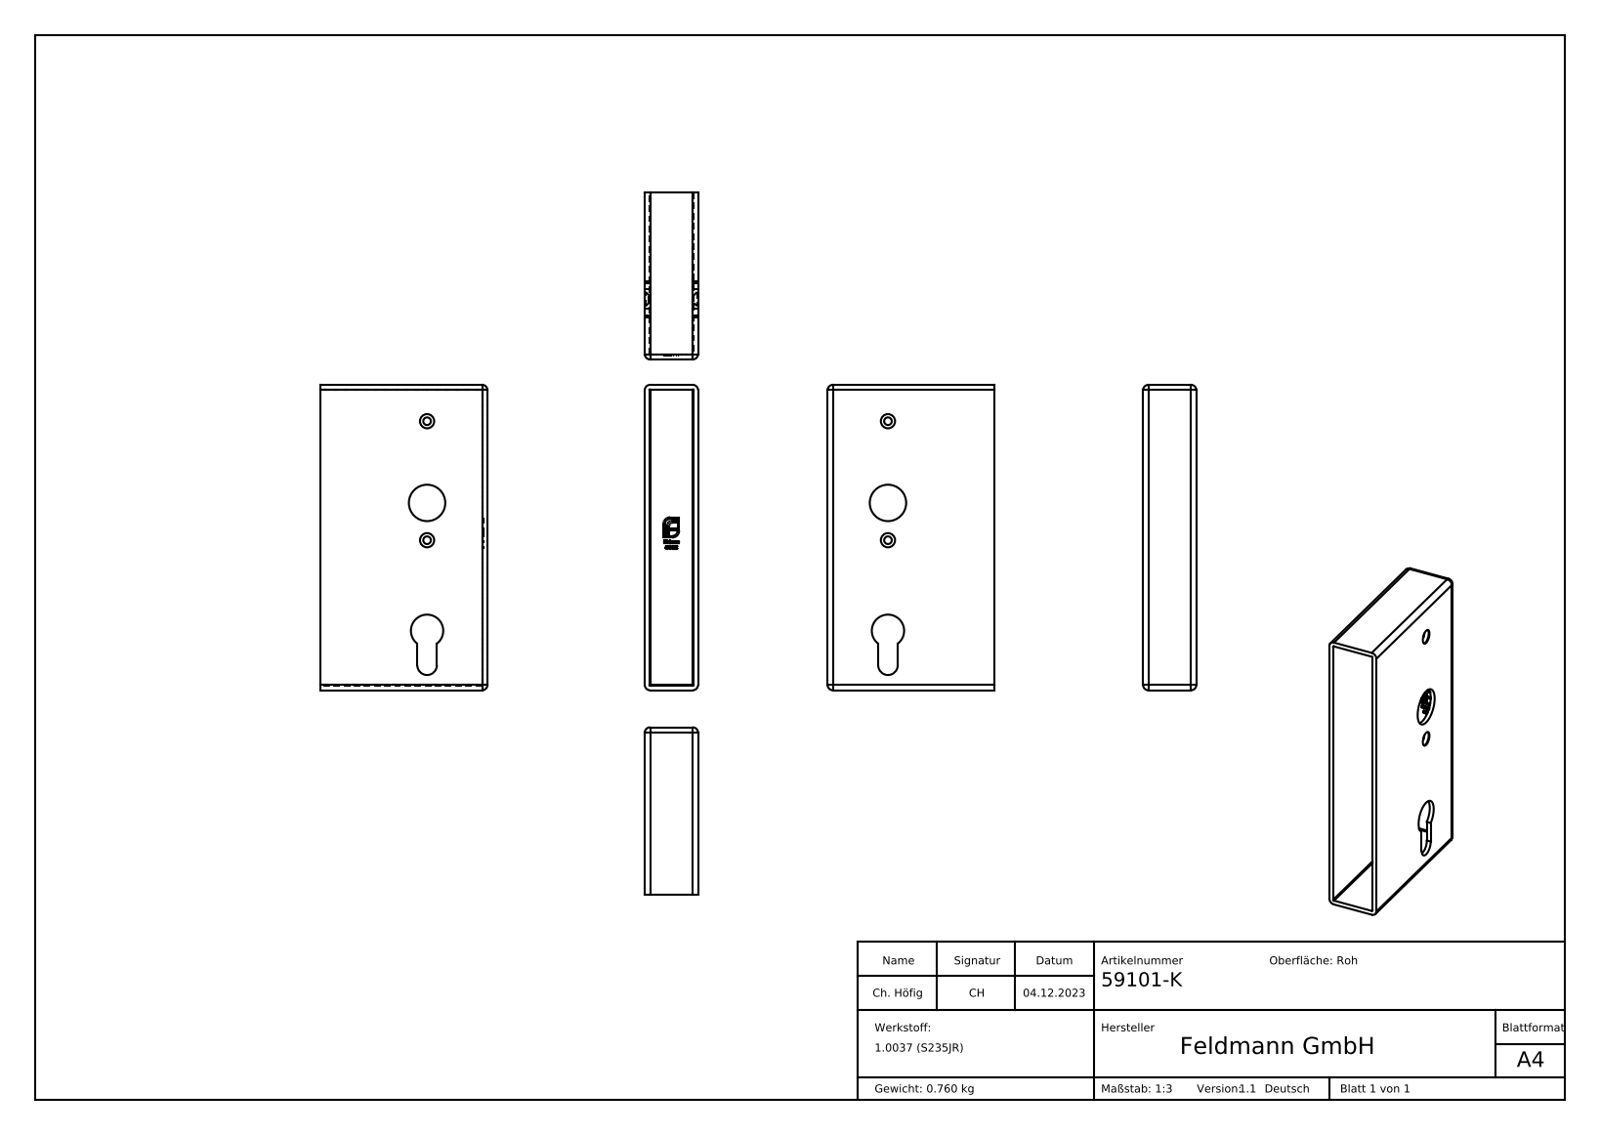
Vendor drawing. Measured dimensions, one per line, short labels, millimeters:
name: 59101-K
written by: SolidWorks 2018 (CONFIG_CONTROL_DESIGN)
unit: mm
bodies: 1 solid, 284 faces (148 planar, 30 cylindrical, 106 other)
size: 172 × 94 × 30
volume: 97 451 mm³; area: 80 000 mm²
holes: 2× ⌀4.3, 2× ⌀8, 1× ⌀20.5
rounds: 8× R0.5, 8× R3, 1× R5.5, 1× R9.1
face distances: 2.5, 27.5, 25, 30, 169.5, 172, 167, 94, 91.5, 39.5
hole spacings: 21, 46, 67
